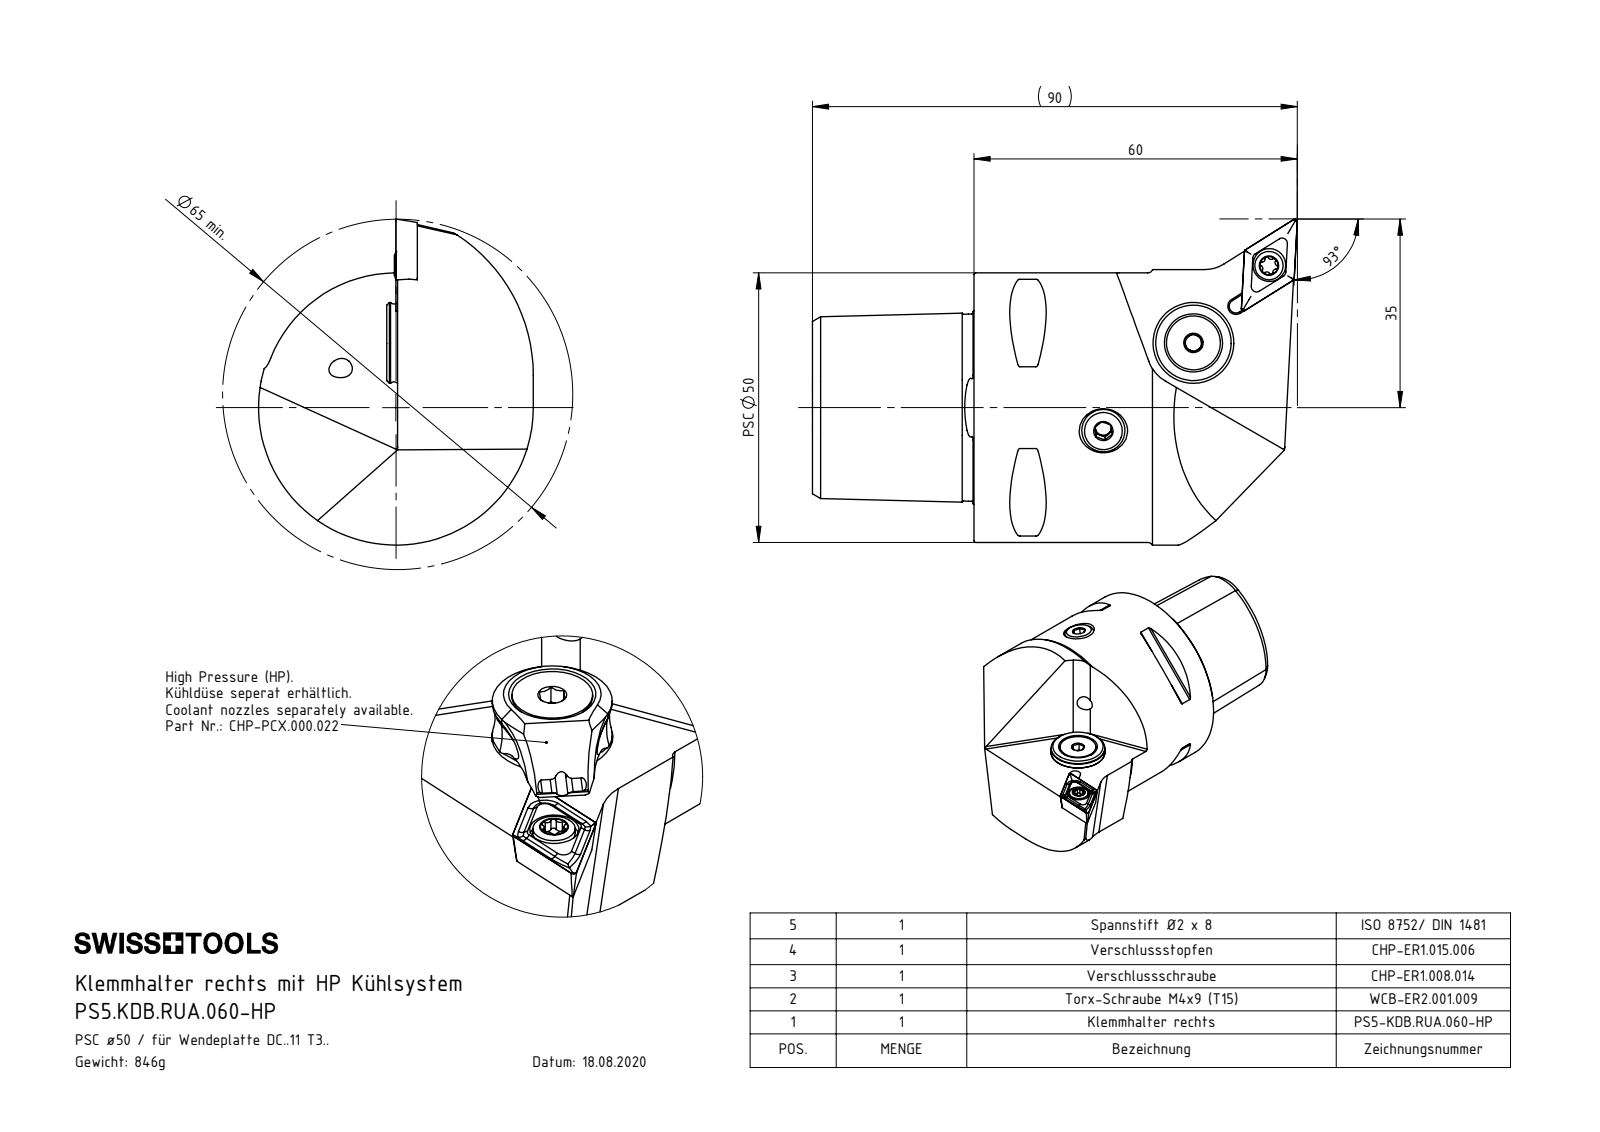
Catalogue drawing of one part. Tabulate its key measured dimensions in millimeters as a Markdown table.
| quantity | value |
| --- | --- |
| part name | DIN 3771 - 13x1; DCMT11T304; DIN 7991 - M5x15; ISO 8752 2x8 (+6 more) |
| STEP written by | SolidWorks 2017 (AUTOMOTIVE_DESIGN) |
| units | millimeters |
| bodies | 8 solids, 376 faces (91 planar, 99 cylindrical, 186 other) |
| overall size | 90 × 60.51 × 51 |
| volume | 107 839 mm³ |
| surface area | 22 697 mm² |
| round holes (diameter × count) | 4.2 × 3, 6.1 × 2, 1.2 × 1, 2 × 1, 2.5 × 1, 3 × 1, 3.3 × 1, 4 × 1, 4.4 × 1, 5 × 1, 5.2 × 1, 7 × 1 |
| round bosses / shafts (diameter × count) | 50 × 1, 15 × 1, 13.4 × 1, 10 × 1, 8 × 1, 5.5 × 1, 5.25 × 1, 5 × 1 |
| partial cylindrical surfaces (radius × count) | 0.5 × 10, 0.34 × 6, 0.59 × 6, 7 × 2, 1.25 × 1, 4 × 1, 25.5 × 1, 31 × 1 |
| main face-to-face distances | 30, 4.5, 19.18, 0.83, 3.67, 44.4, 20.7, 21.53, 25.2, 20 |
| hole center spacings | 4.5, 17.07, 17.18, 20.05, 20.17, 26, 31.13, 33.19 |
